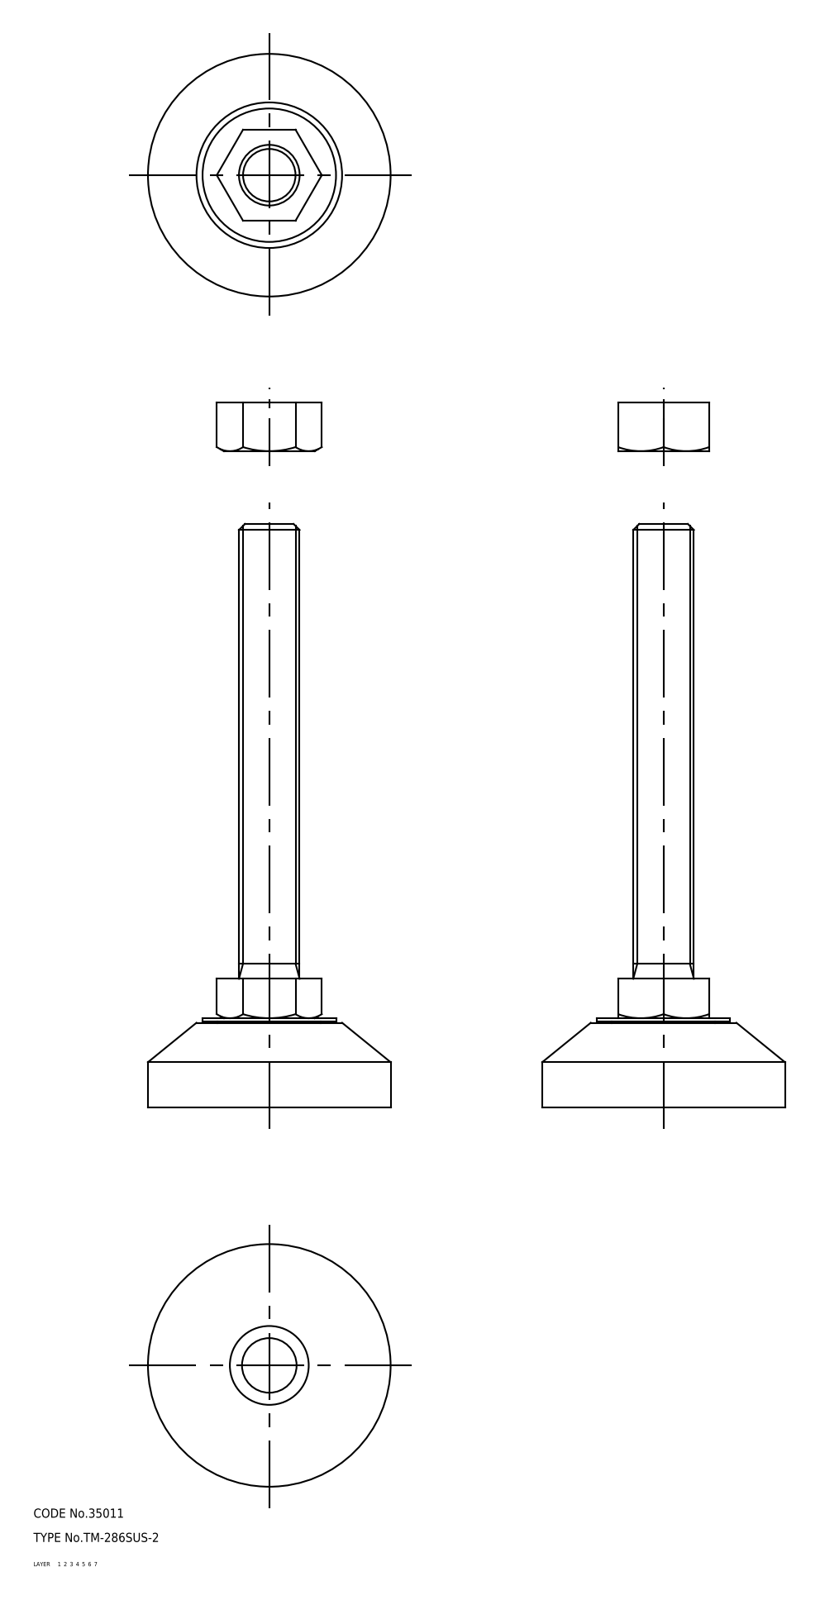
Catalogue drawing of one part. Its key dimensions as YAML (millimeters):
part_name: "67111642; 67111655"
step_written_by: "CADfix (AUTOMOTIVE_DESIGN)"
units: millimeters
bodies: {solids: 2, faces: 52, planar: 0, cylindrical: 0, other: 52}
overall_size: [192.5, 80, 80]
volume: 182161
surface_area: 31361
